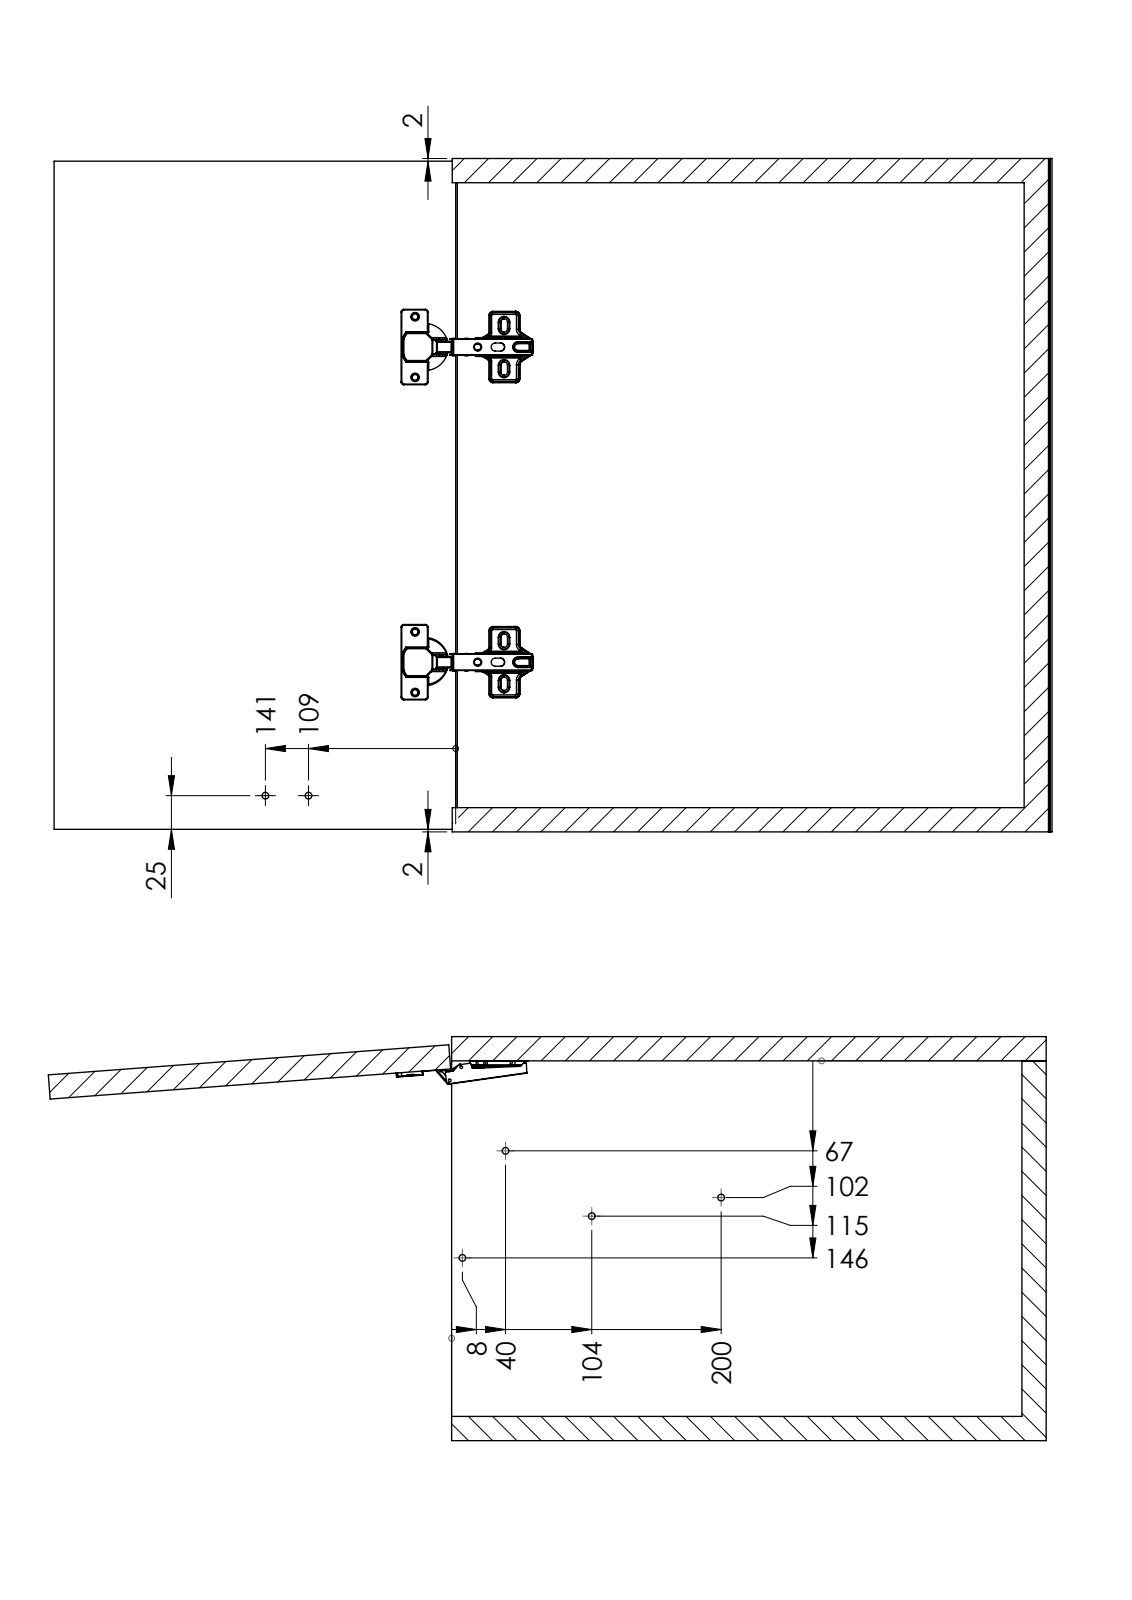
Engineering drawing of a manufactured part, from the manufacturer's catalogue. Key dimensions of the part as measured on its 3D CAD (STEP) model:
Part name (STEP PRODUCT): Airtic_Podnonik; Podnosnik_oslona__A; Podnosnik_zaczep__A; Podnosnik_wspornik__A (+1 more)
STEP written by: SolidWorks 2017 (AUTOMOTIVE_DESIGN)
Units: millimetres
Bodies: 4 solids, 1942 faces (823 planar, 310 cylindrical, 809 other)
Overall size (bounding box): 228.48 × 94.22 × 19.19
Volume: 314 319 mm³ · Surface area: 115 202 mm²
Round holes (diameter × count): ⌀4.27 ×4, ⌀4.48 ×2, ⌀9.81 ×2
Round bosses / shafts (diameter × count): ⌀4.94 ×1, ⌀4 ×1
Partial cylindrical surfaces — rounded edges, fillets, slot ends (radius × count): R0.2 ×53, R1 ×36, R0.5 ×12, R2.5 ×7, R1.35 ×6, R0.6 ×4, R8 ×4, R2 ×3
Main face-to-face distances: 1.3, 17.8, 19.1, 92.92, 91.62, 94.22, 1.47, 92.75, 91.45, 25.68
Hole centre spacings: 32, 80.3, 85.7, 96.99, 100.88, 163.72, 197.16
